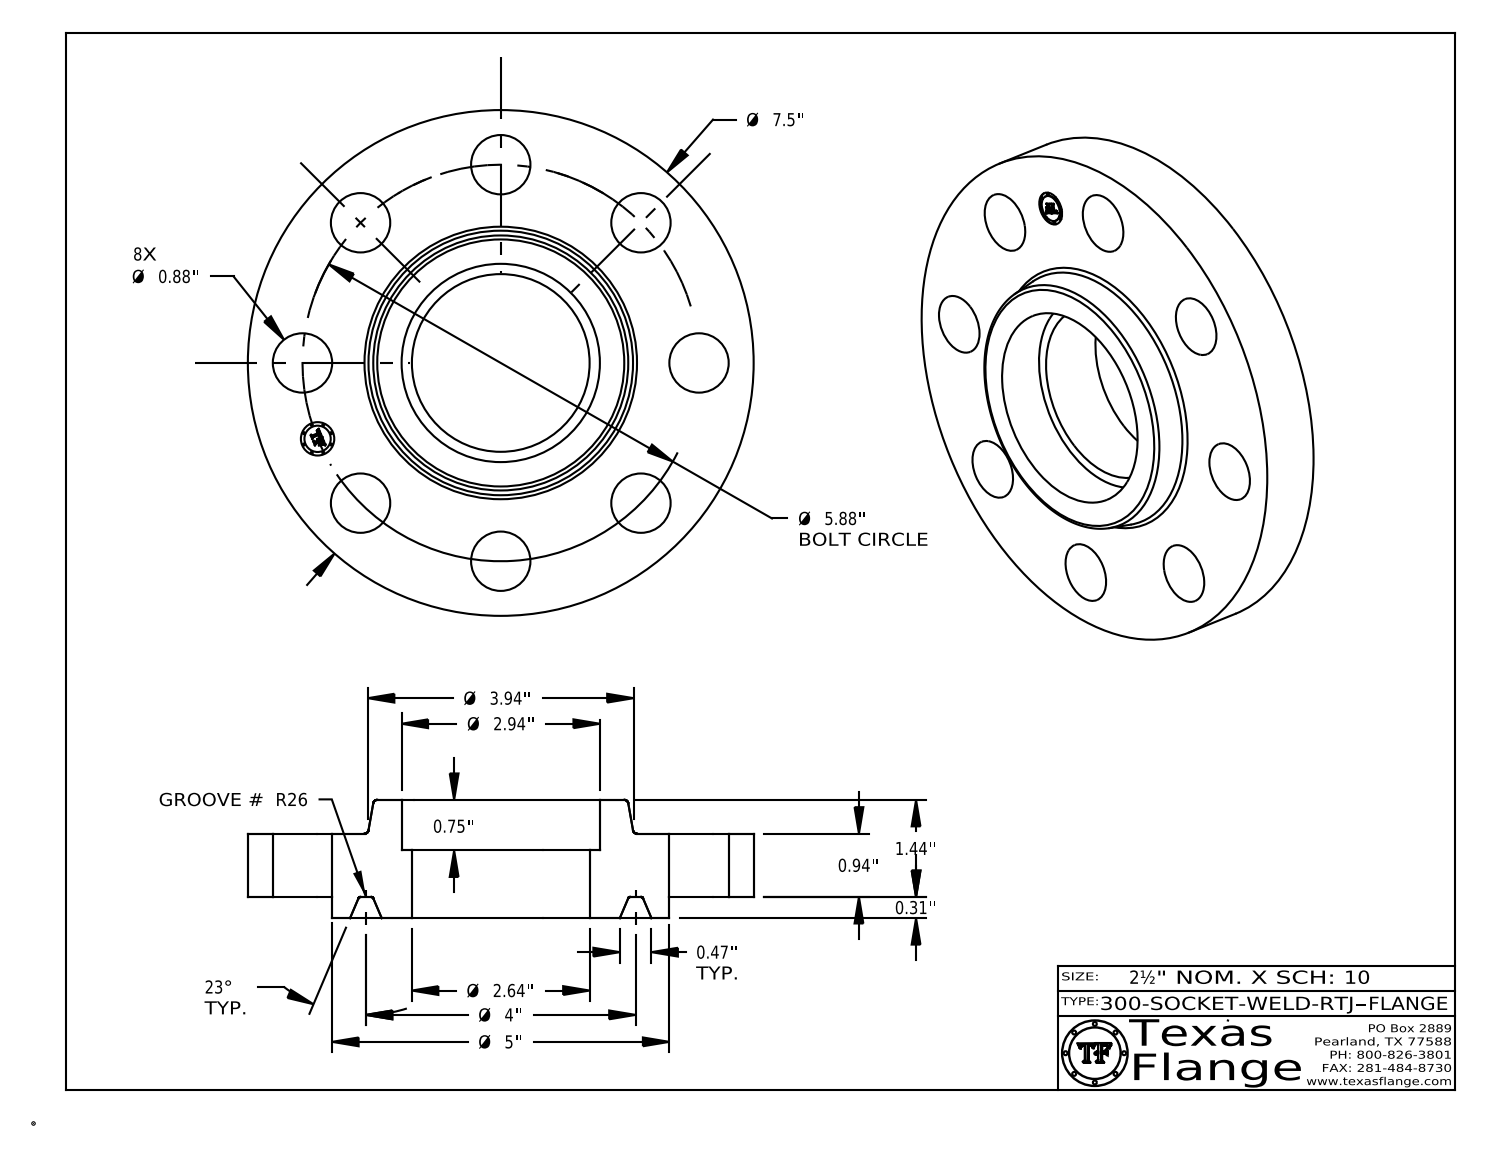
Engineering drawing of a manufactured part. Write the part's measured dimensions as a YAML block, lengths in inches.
part_name: "300-SOCKET-WELD-RTJ"
step_written_by: "CATIA V5 STEP AP214 (AUTOMOTIVE_DESIGN)"
units: inches
bodies: {solids: 1, faces: 430, planar: 372, cylindrical: 44, other: 14}
overall_size: [7.5, 7.5, 1.753]
volume: 37.05
surface_area: 140.7
round_holes:
  - {diameter: 0.88, count: 8}
  - {diameter: 0.495, count: 1}
  - {diameter: 2.635, count: 1}
  - {diameter: 2.94, count: 1}
round_bosses_or_shafts:
  - {diameter: 0.03, count: 8}
  - {diameter: 7.5, count: 1}
  - {diameter: 5, count: 1}
  - {diameter: 0.39, count: 1}
face_to_face_distances: [0.94, 0.313, 1.253, 1.753, 1.44, 0.5, 1.003, 0.69, 0.25, 0.75]
hole_center_spacings: [2.25, 5.432, 2.94, 2.94, 4.157, 4.158, 3.267, 5.88]
